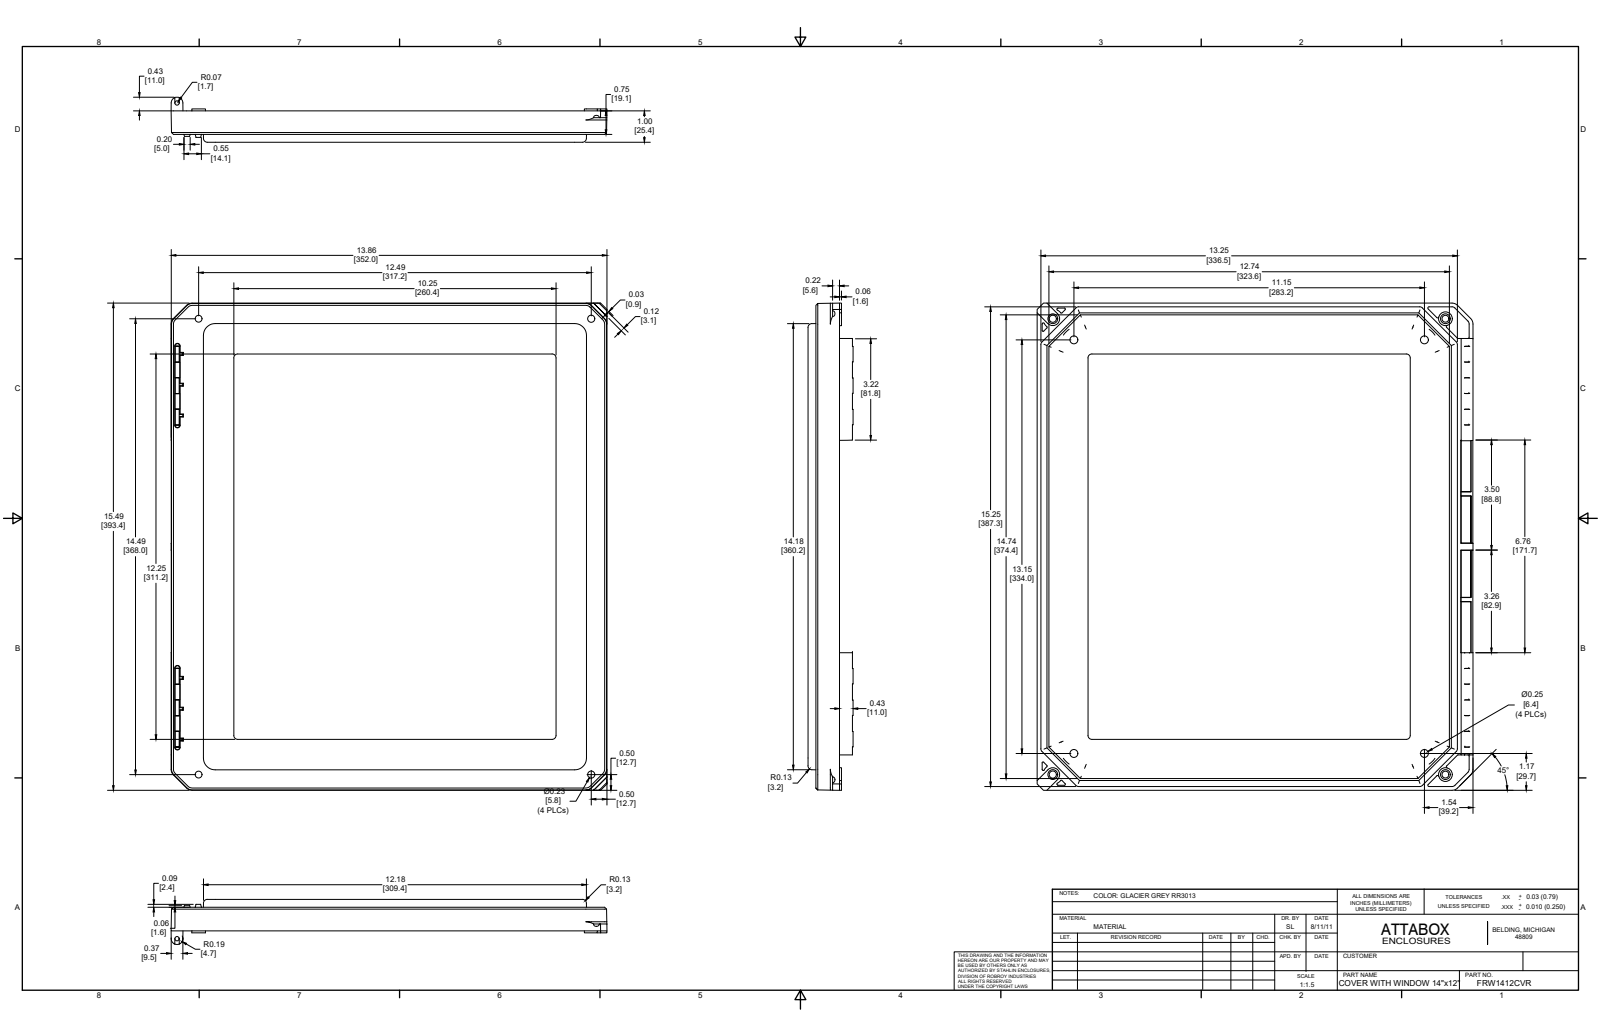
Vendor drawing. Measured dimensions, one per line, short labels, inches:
name: FRW1412CVR
written by: SolidWorks 2019 (AUTOMOTIVE_DESIGN)
unit: in
bodies: 1 solid, 627 faces (263 planar, 204 cylindrical, 160 other)
size: 15.489 × 13.864 × 1.434
volume: 27.4 in³; area: 319.8 in²
holes: 4× ⌀0.253, 2× ⌀0.219, 2× ⌀0.227, 2× ⌀0.313, 1× ⌀0.137
bosses: 2× ⌀0.435
rounds: 27× R0.03, 18× R0.01, 16× R0.096, 16× R0.125, 14× R0.063, 10× R0.04, 10× R0.062, 9× R0.06
face distances: 0.125, 0.25, 0.125, 0.375, 0.75, 1, 0.625, 0.875, 0.375, 0.638
hole spacings: 13.836, 0.946, 0.947, 11.15, 11.838, 11.839, 12.489, 13.15
